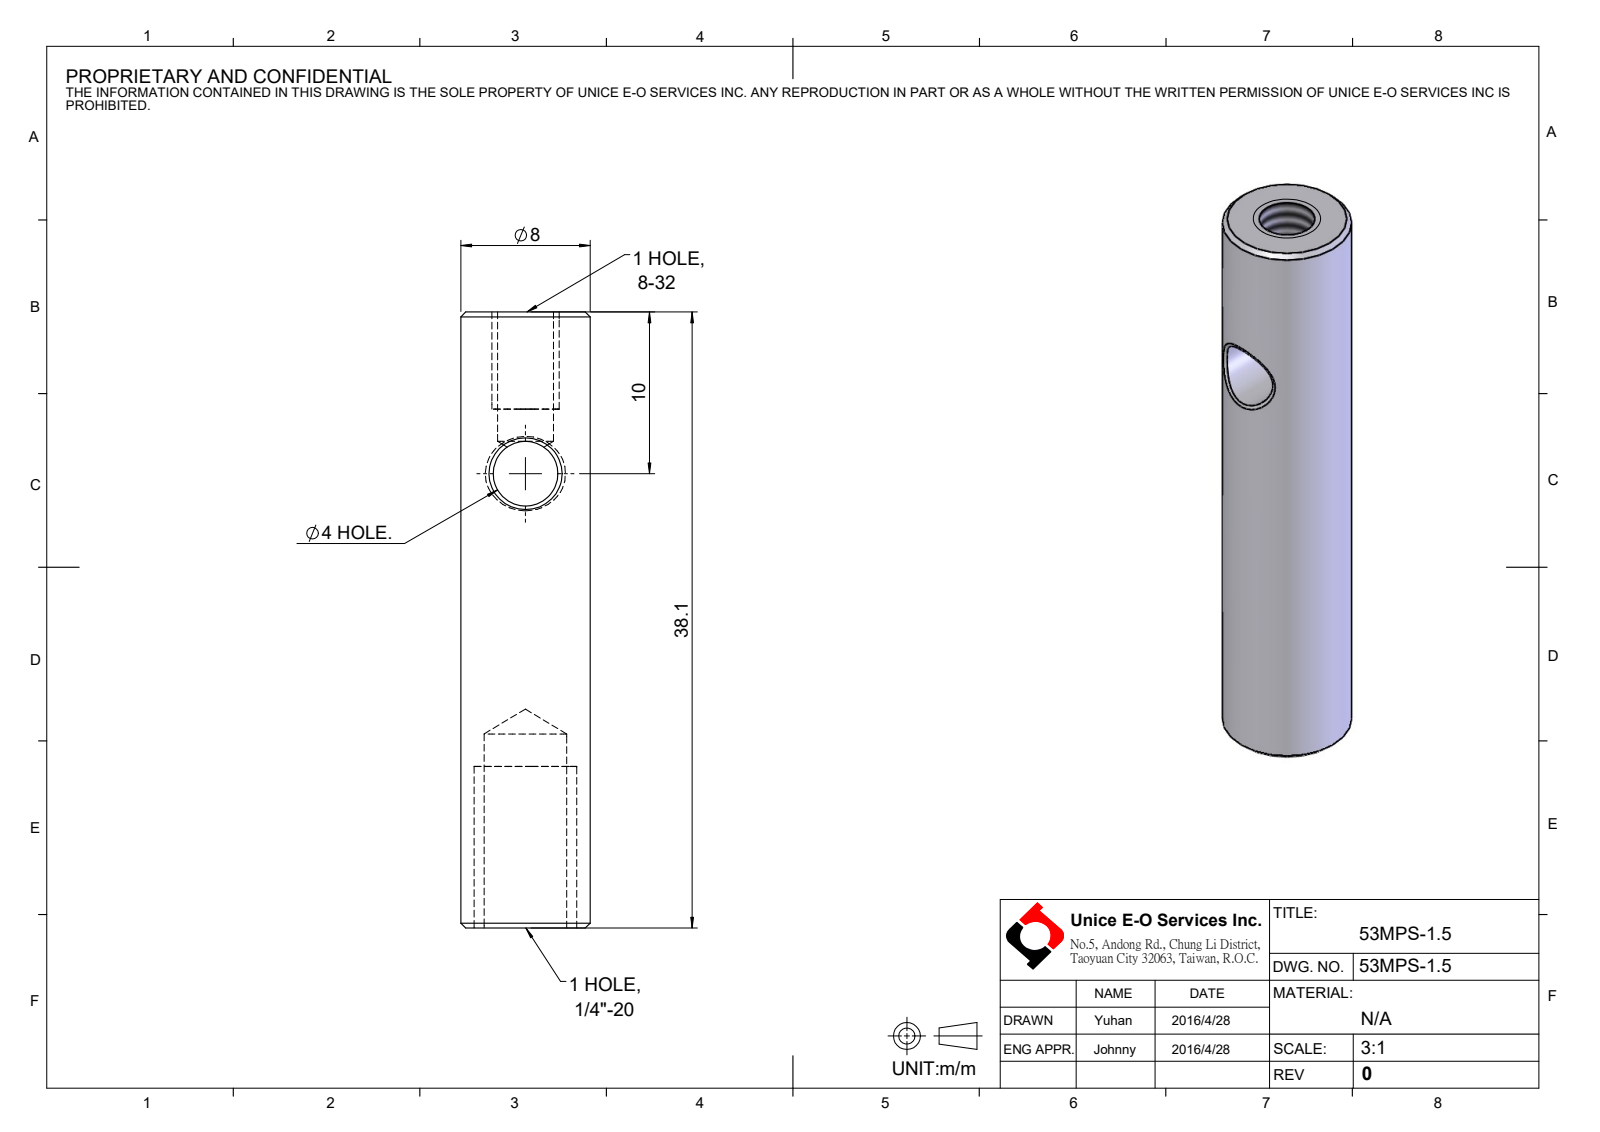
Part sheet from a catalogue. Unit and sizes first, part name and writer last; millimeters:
Units: millimetres
Overall size (bounding box): 38.1 × 8 × 8
Round holes (diameter × count): ⌀3.45 ×1, ⌀4 ×1, ⌀5.11 ×1
Round bosses / shafts (diameter × count): ⌀8 ×1
Main face-to-face distances: 38.1
Volume: 1 482 mm³ · Surface area: 1 381 mm²
Bodies: 1 solid, 23 faces (2 planar, 8 cylindrical, 13 other)
Part name (STEP PRODUCT): 53MPS-1.5
STEP written by: SolidWorks 2016 (CONFIG_CONTROL_DESIGN)
